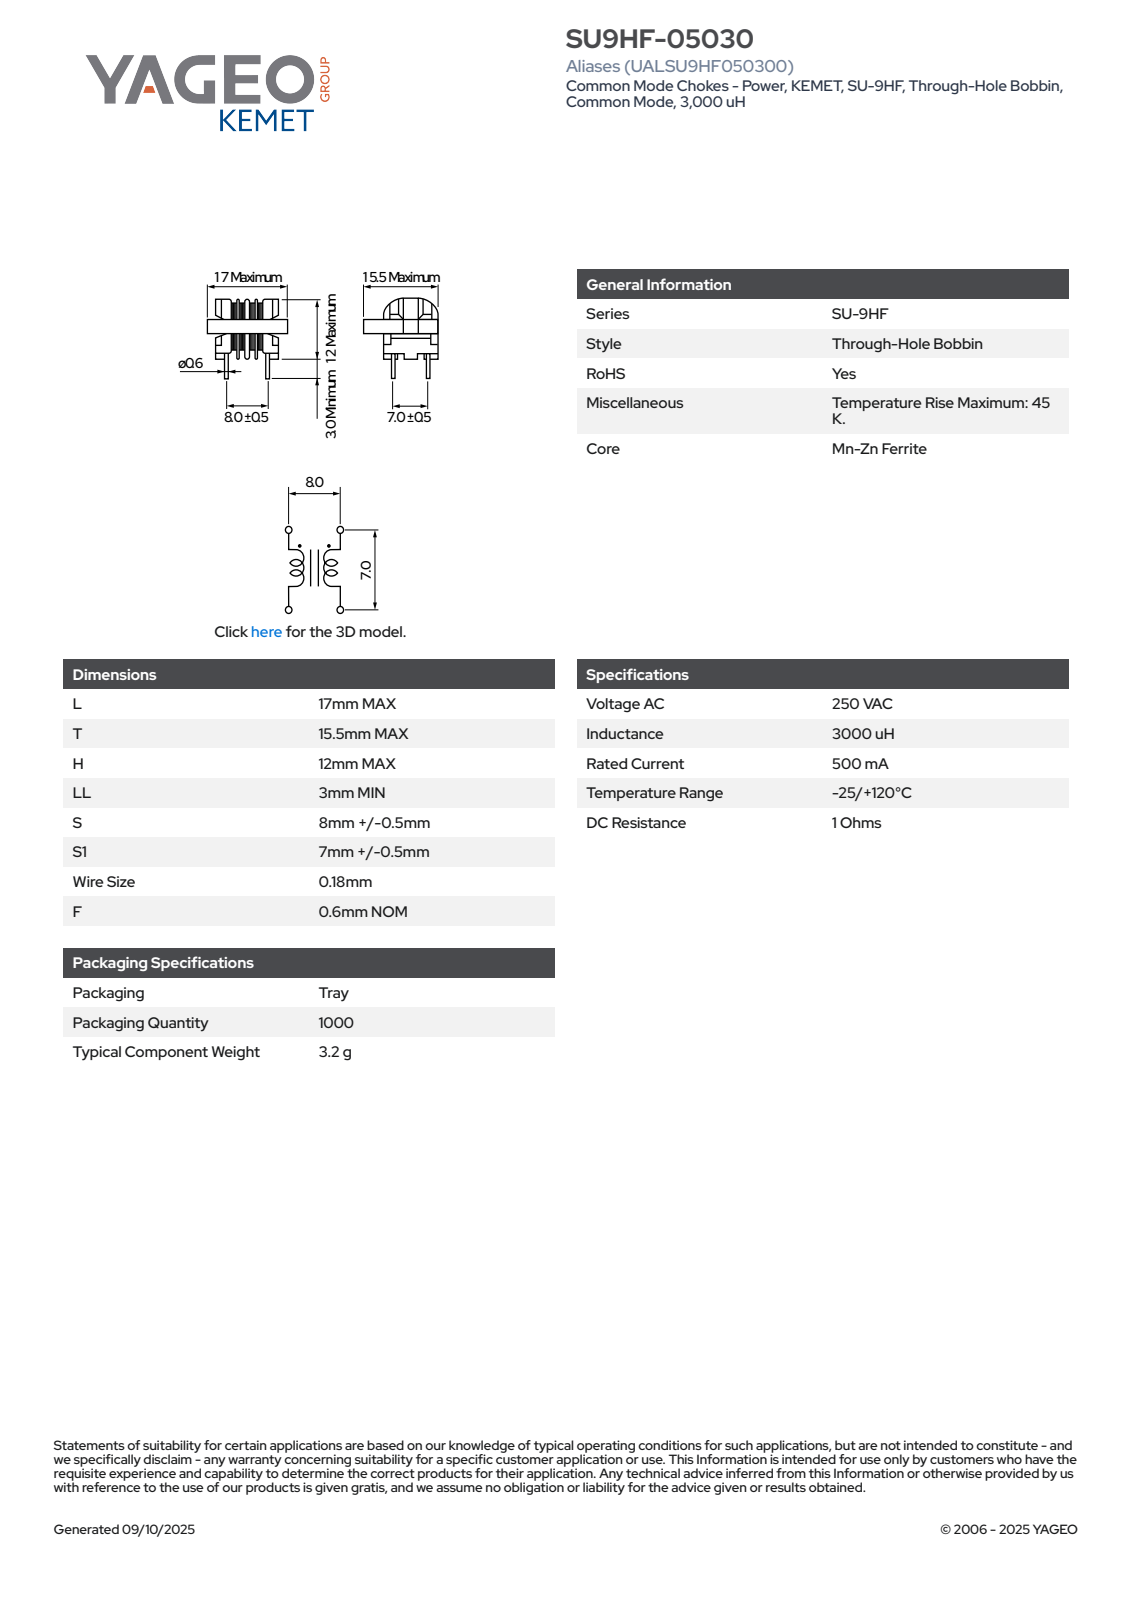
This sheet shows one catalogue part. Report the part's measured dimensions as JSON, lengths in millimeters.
{"part_name": "SU9HF(MAX-LOGO)", "step_written_by": "SolidWorks 2018 (AUTOMOTIVE_DESIGN)", "units": "millimeters", "bodies": {"solids": 1, "faces": 489, "planar": 233, "cylindrical": 168, "other": 88}, "overall_size": [17, 16.5, 15.5], "volume_mm3": 1039, "surface_area_mm2": 1714, "round_bosses_or_shafts": [[0.6, 4]], "partial_cylinders_radius": [[0.15, 64], [0.3, 50], [0.5, 12], [0.2, 4], [1, 2], [2, 2], [3.5, 2]], "face_to_face_distances": [2.8, 3.68, 0.8, 3.67, 2.15, 2.85, 8.7, 7.5, 1.24, 2.04]}
